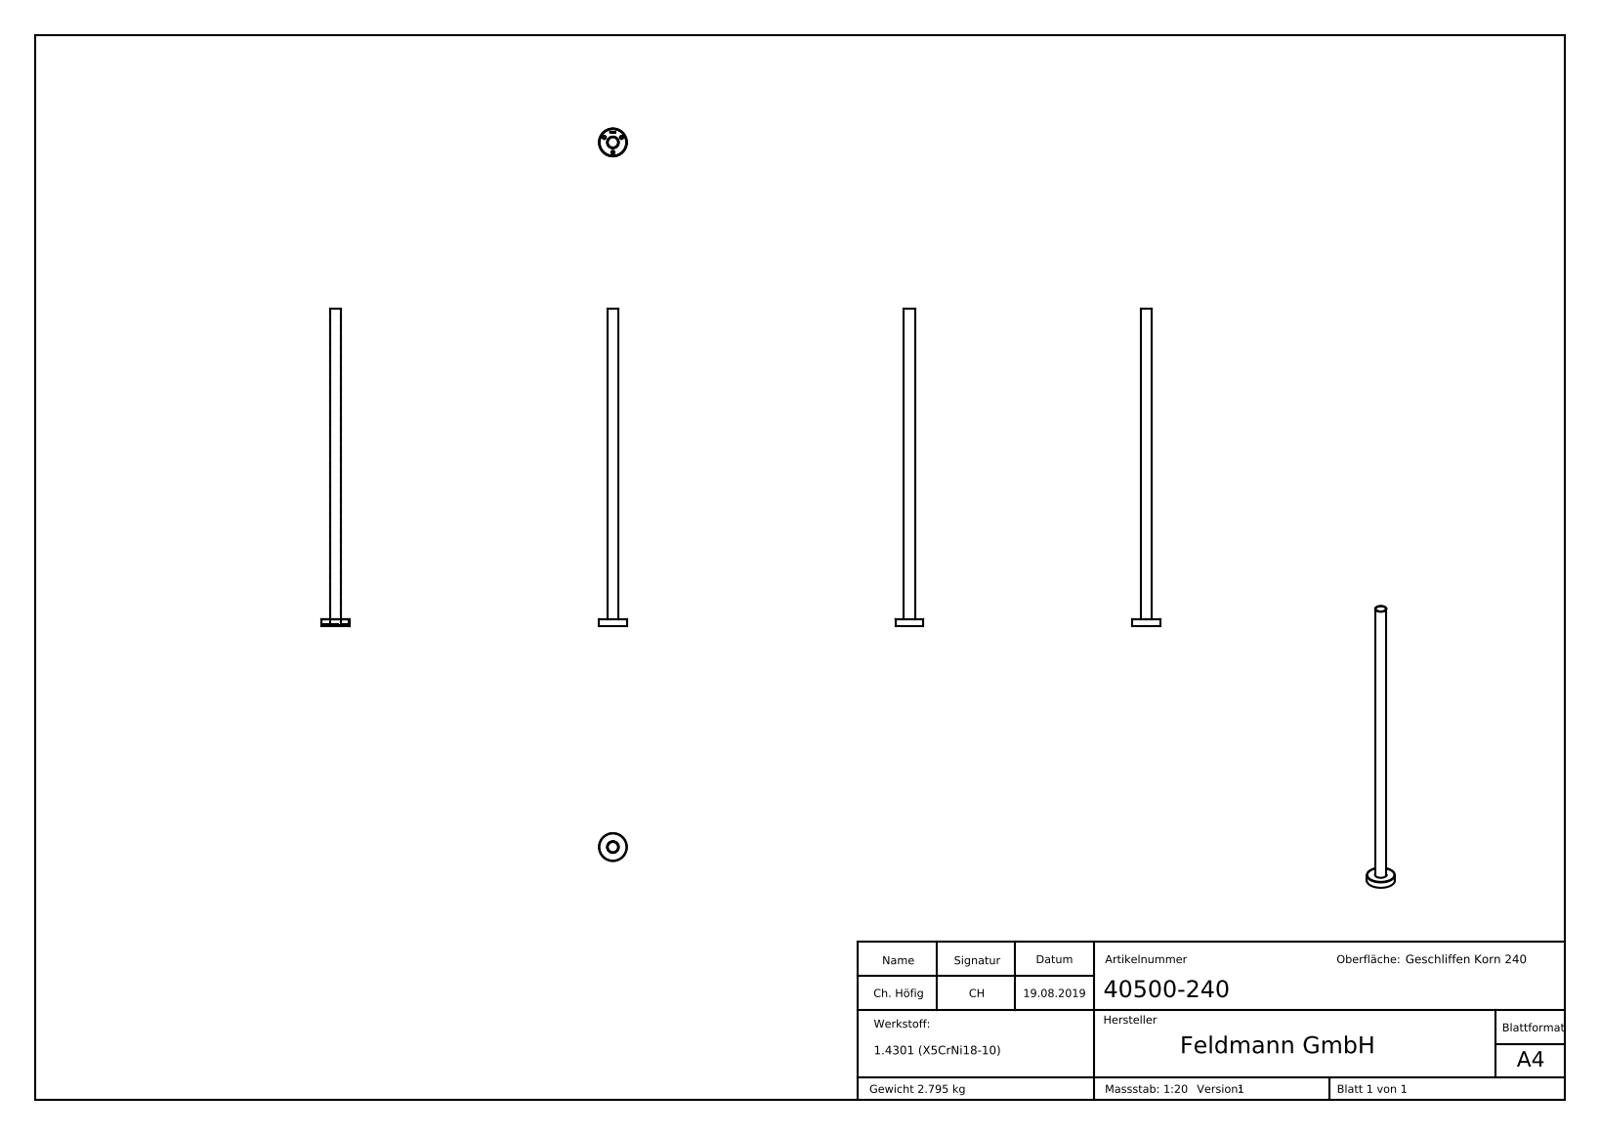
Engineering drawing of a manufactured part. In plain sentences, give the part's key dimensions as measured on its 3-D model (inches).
The part is named "50152-240_50152-240; 40500-240; 54106-240_54106-240; 405XX-240 Teil1_40500-240 Teil1". Its 3-D file was written by "SolidWorks 2015 (CONFIG_CONTROL_DESIGN)". It is 3 solids with 267 faces: 129 planar, 20 cylindrical and 118 other. Overall it measures 46.85 by 4.134 by 4.134 inches. Its volume is 21.59 cubic inches and its surface area 540 square inches. Round holes: 3 of diameter 0.433, 1 of diameter 1.512, 1 of diameter 1.685, 1 of diameter 1.693, 1 of diameter 4.055. Round bosses or shafts: 1 of diameter 4.134, 1 of diameter 3.937, 1 of diameter 1.669. The main face-to-face distances are 0.039, 0.945, 0.984, 0.236, 0.709, 0.748, 46.85, 46.614, 45.906, 45.866. The hole center spacings are 1.476, 2.557, 2.557.
